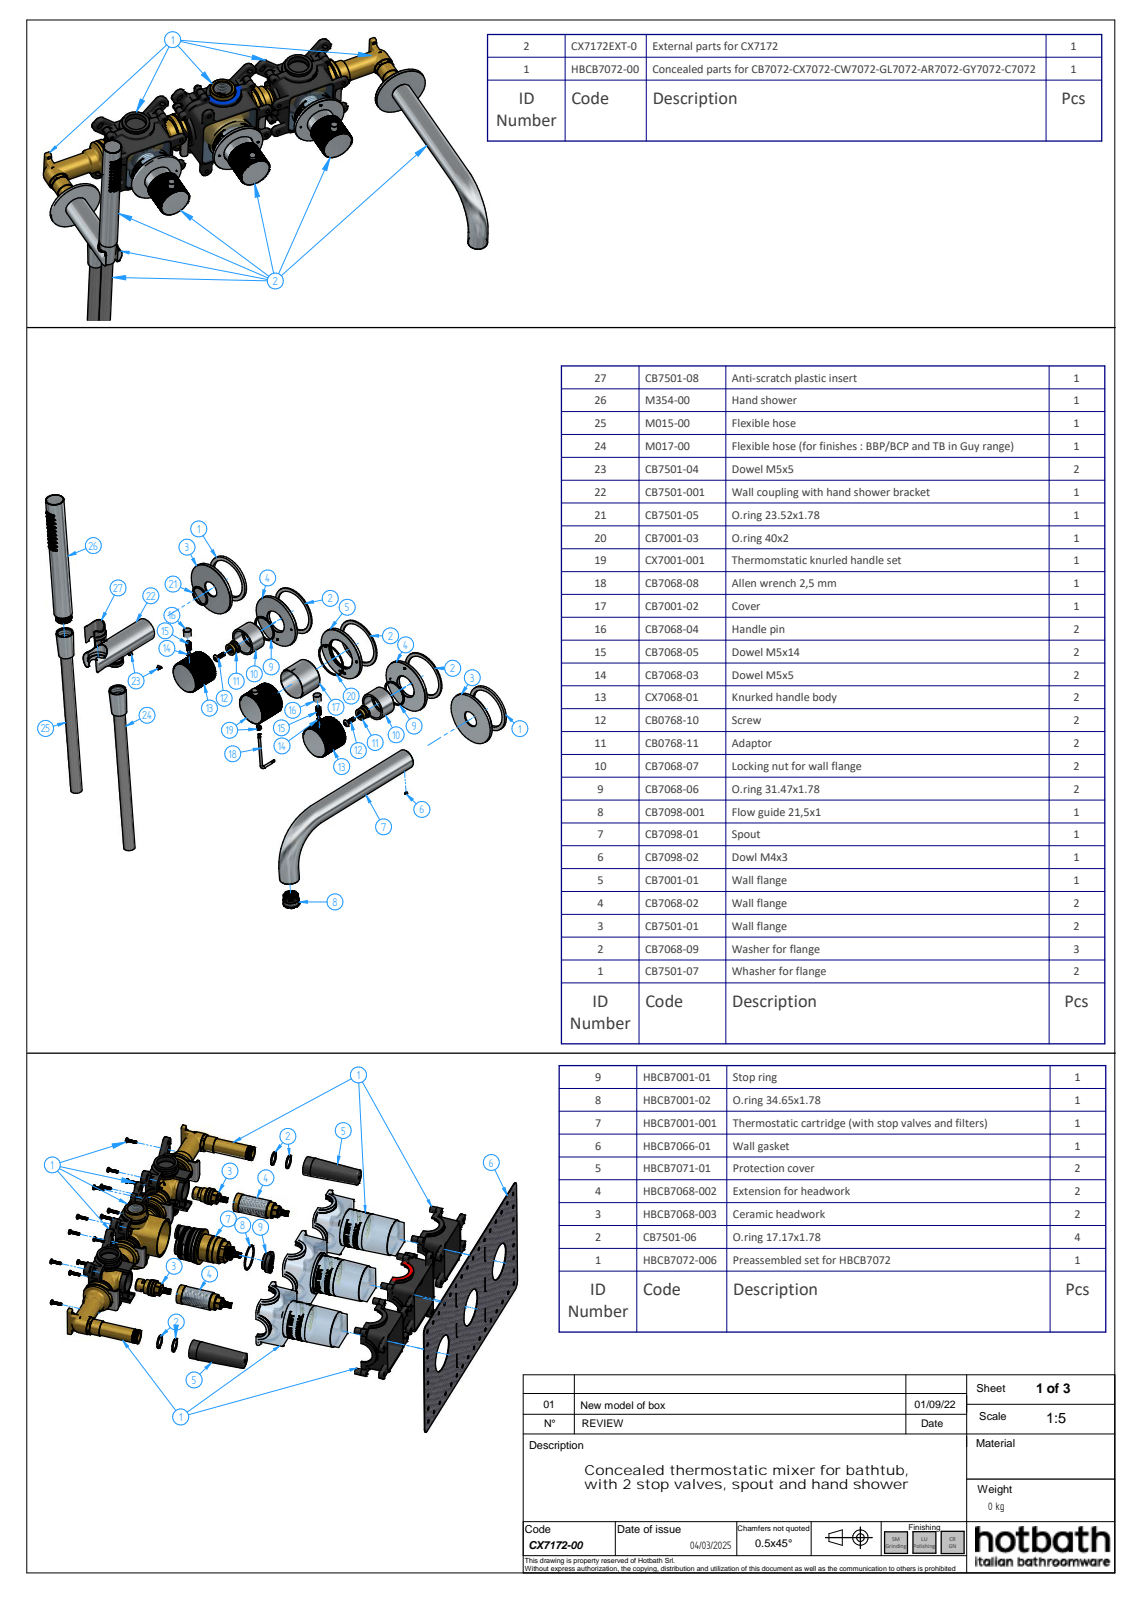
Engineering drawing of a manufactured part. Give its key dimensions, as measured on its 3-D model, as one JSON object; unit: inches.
{"part_name": "CX7172EXT-00; CB7098-01; CB7098-02; CB7098-001 (+8 more)", "step_written_by": "Solid Edge (AUTOMOTIVE_DESIGN)", "units": "inches", "bodies": {"solids": 27, "faces": 19805, "planar": 580, "cylindrical": 4113, "other": 15112}, "overall_size": [21.732, 18.371, 10.165], "volume_in3": 20.33, "surface_area_in2": 364.5, "round_holes": [[0.126, 41], [0.118, 5], [0.163, 5], [0.138, 4], [0.205, 3], [0.402, 3], [0.866, 3], [2.638, 3], [0.177, 2], [0.598, 2], [0.65, 2], [0.733, 2]], "round_bosses_or_shafts": [[2.835, 5], [2.244, 3], [1.654, 3], [0.394, 3], [2.047, 2], [1.457, 2], [1.024, 2], [0.63, 2]], "partial_cylinders_radius": [[0.008, 22], [0.02, 15], [0.012, 6], [0.014, 4], [0.138, 4], [0.023, 3], [0.03, 3], [0.009, 2]], "face_to_face_distances": [0.157, 0.059, 0.118, 0.039, 0.098, 0.023, 0.017, 0.076, 0.135, 0.217], "hole_center_spacings": [0.284, 0.498, 0.236, 0.472, 0.726, 0.157, 0.709, 0.958]}
